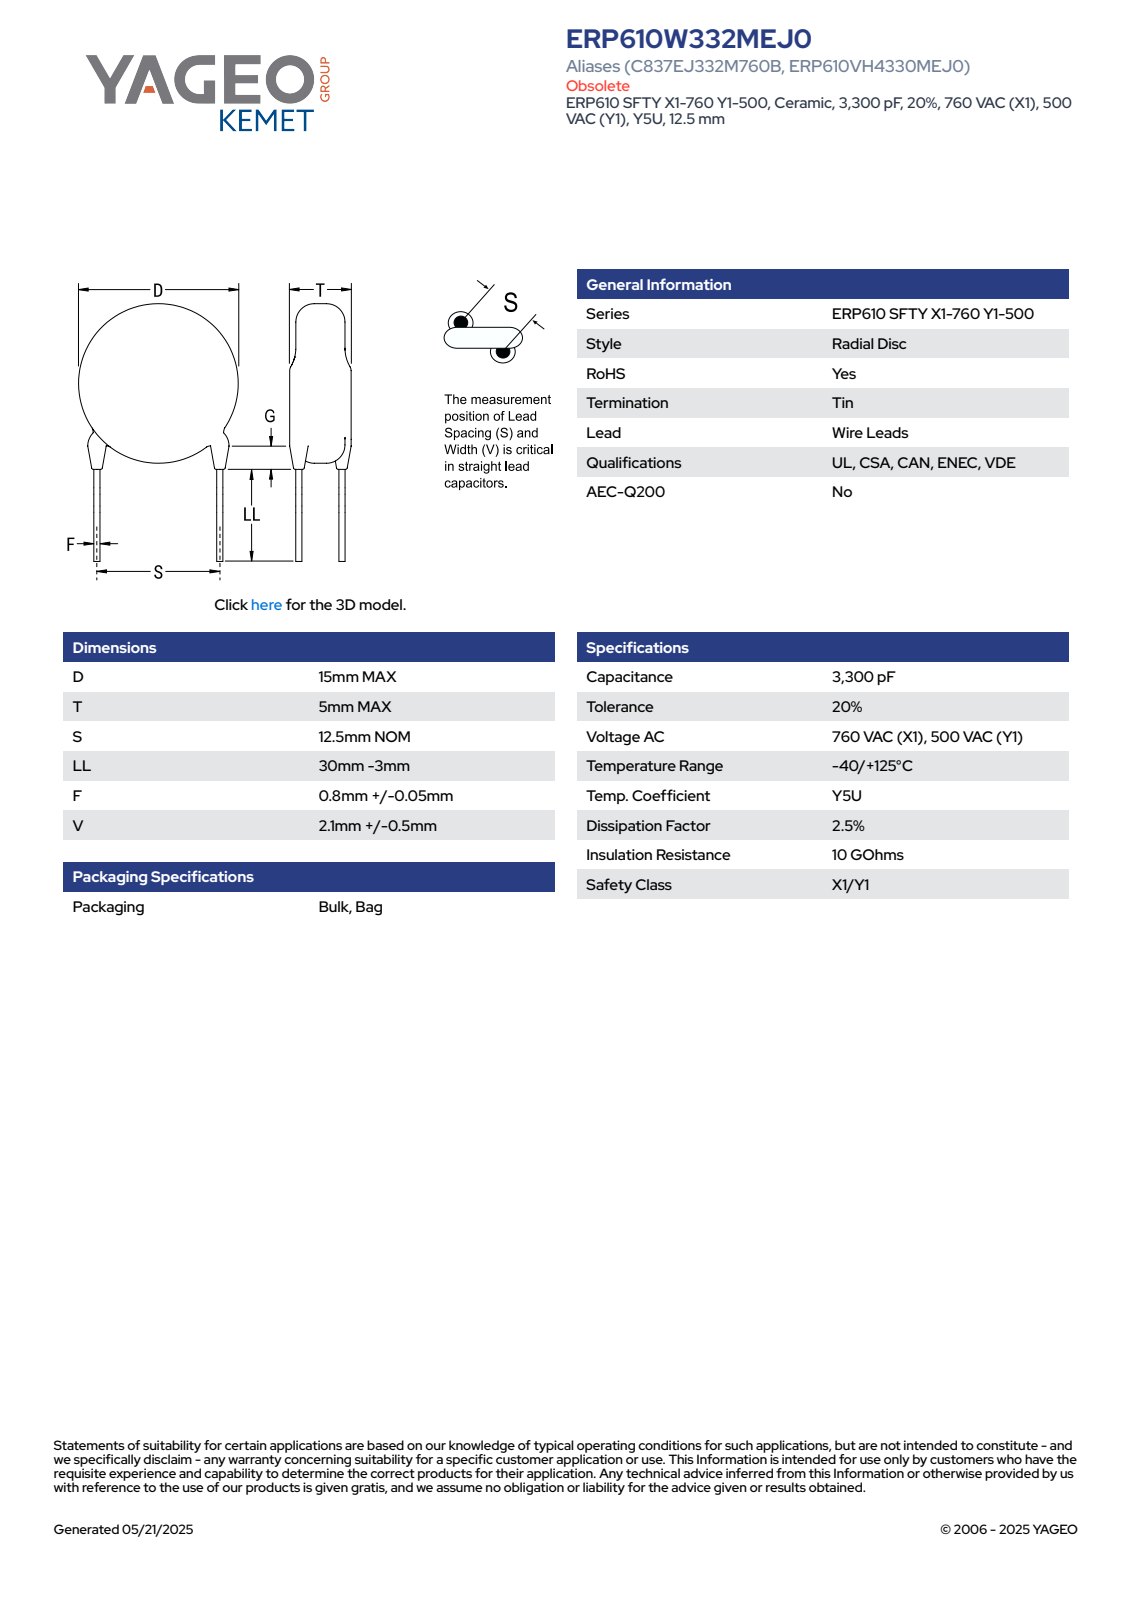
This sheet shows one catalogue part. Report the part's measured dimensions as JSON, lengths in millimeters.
{"part_name": "CCD_KST_15X5_D15T5S12.5LL27F0.85G3V2.6", "step_written_by": "SolidWorks 2014 (AUTOMOTIVE_DESIGN)", "units": "millimeters", "bodies": {"solids": 4, "faces": 83, "planar": 61, "cylindrical": 10, "other": 12}, "overall_size": [42.17, 15, 5], "volume_mm3": 898, "surface_area_mm2": 726, "round_bosses_or_shafts": [[0.85, 4], [15, 1]], "face_to_face_distances": [5, 35.6, 33.74, 1.86, 0.35, 0.51, 7.62, 1.51, 1.16, 0.34]}
